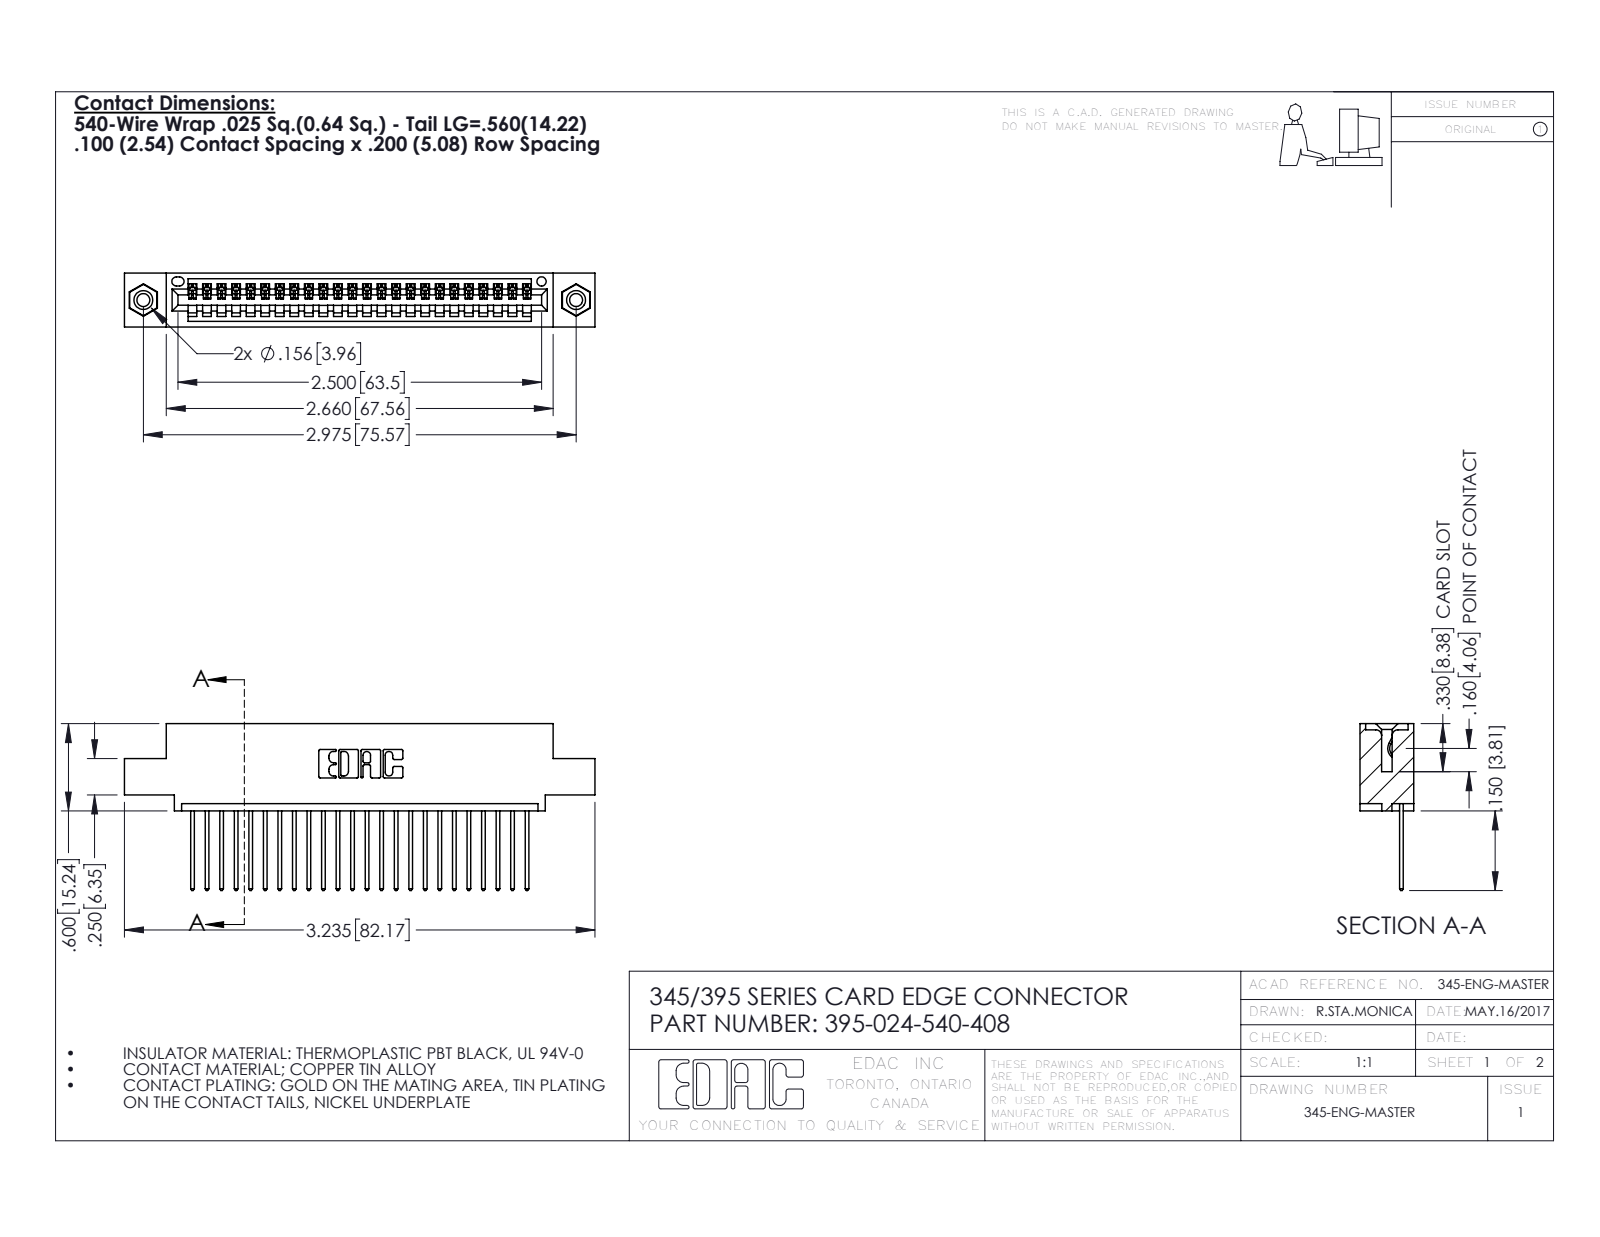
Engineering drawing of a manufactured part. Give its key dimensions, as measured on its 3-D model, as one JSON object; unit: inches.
{"part_name": "345 Part_0.110 Offset - 0.156 Dia-TI; 395-024-540-408; 345-292-001_345-293-140; 345-250-001_345-250-003-102", "step_written_by": "SolidWorks 2016 (CONFIG_CONTROL_DESIGN)", "units": "inches", "bodies": {"solids": 27, "faces": 1582, "planar": 1076, "cylindrical": 490, "other": 16}, "overall_size": [3.235, 1.147, 0.37], "volume_in3": 0.464, "surface_area_in2": 15.81, "round_holes": [[0.089, 2], [0.125, 2], [0.156, 2], [0.064, 1]], "round_bosses_or_shafts": [[0.155, 2]], "partial_cylinders_radius": [[0.006, 48], [0.01, 48], [0.01, 22], [0.007, 6], [0.031, 6], [0.026, 3], [0.031, 2], [0.04, 2]], "face_to_face_distances": [0.072, 0.298, 0.37, 0.2, 0.098, 0.272, 0.025, 0.225, 0.149, 0.072], "hole_center_spacings": [0.27, 2.741, 2.975]}
